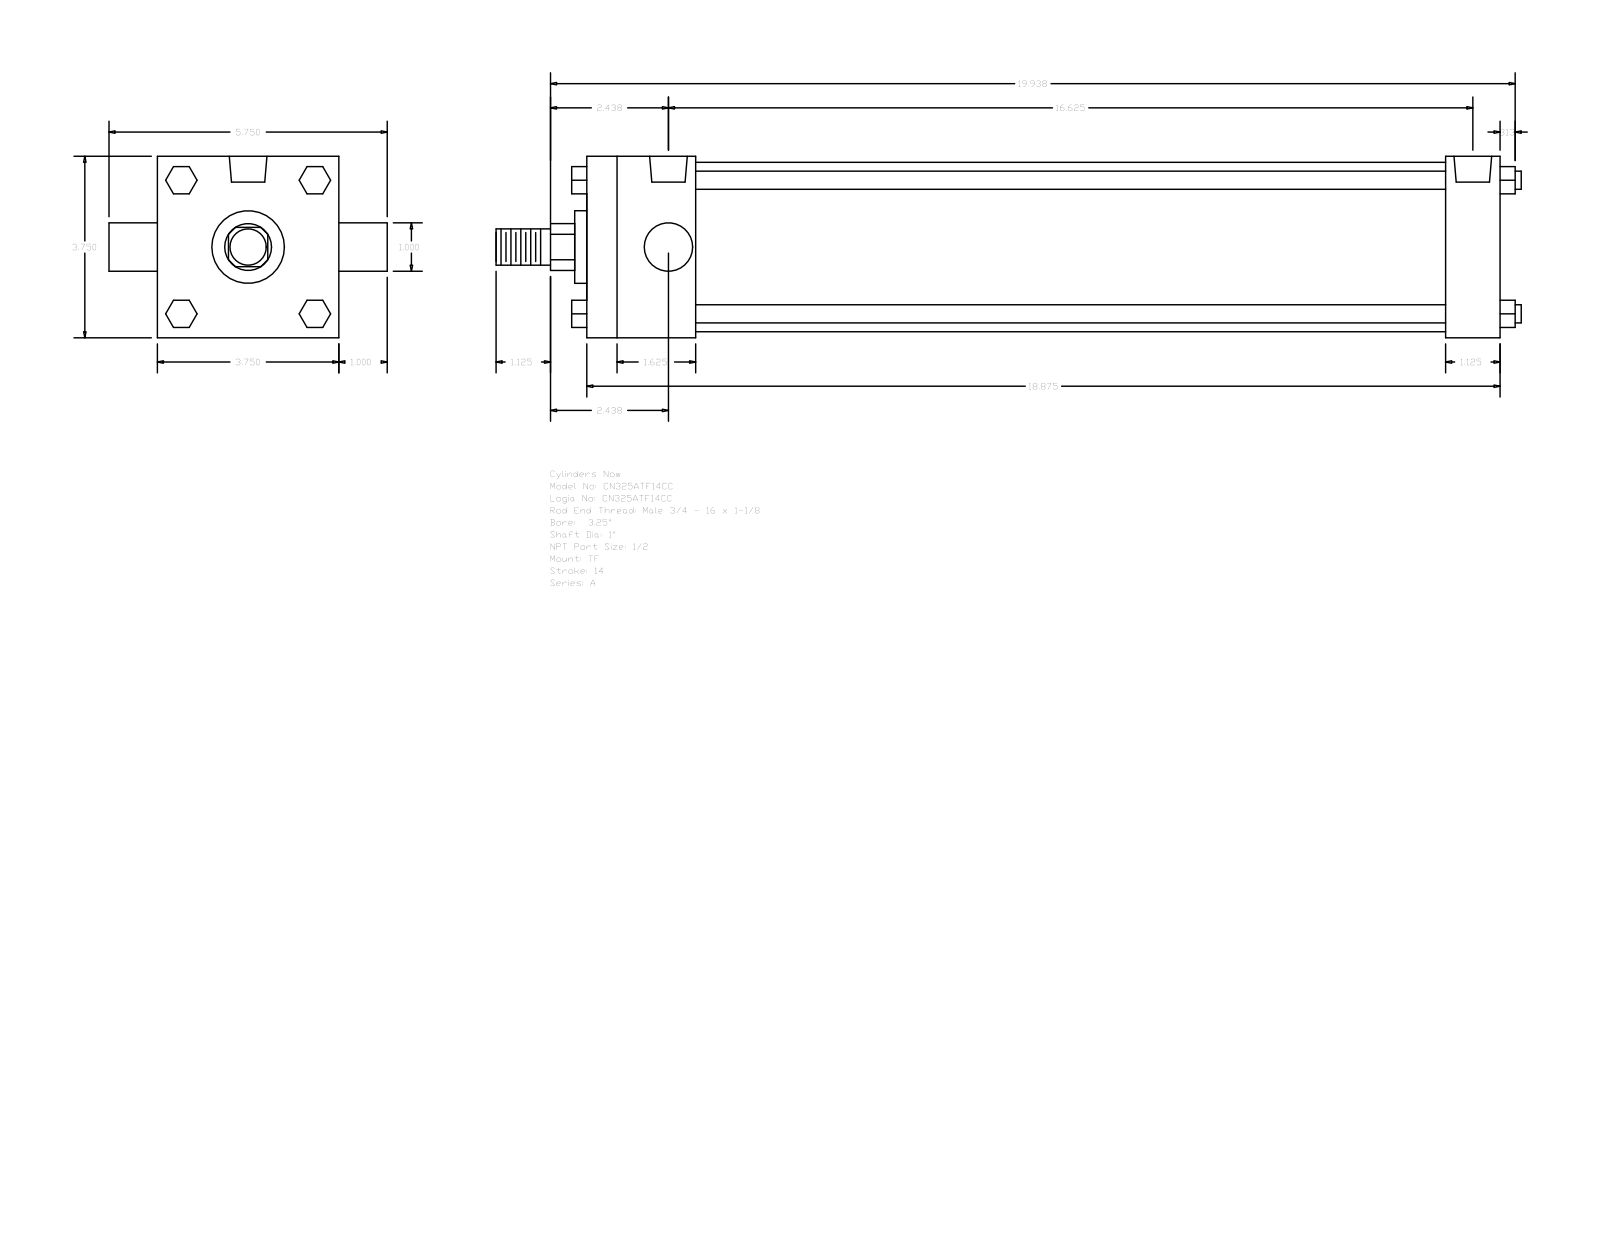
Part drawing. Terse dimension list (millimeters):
name: A_TF__0325_1
written by: GSSL Pune (CONFIG_CONTROL_DESIGN)
unit: mm
bodies: 0 solids, 120 faces (92 planar, 28 cylindrical, 0 other)
size: 538.16 × 146.05 × 95.25
holes: 3× ⌀8.73, 2× ⌀19.77
bosses: 4× ⌀9.53, 2× ⌀25.4, 1× ⌀88.9, 1× ⌀38.1, 1× ⌀19.05
rounds: 1× R12.29
face distances: 95.24, 479.43, 57.15, 450.85, 393.7, 422.28, 28.58, 14.28, 35.05, 60.71
hole spacings: 3.18, 419.1, 415.92, 422.28
